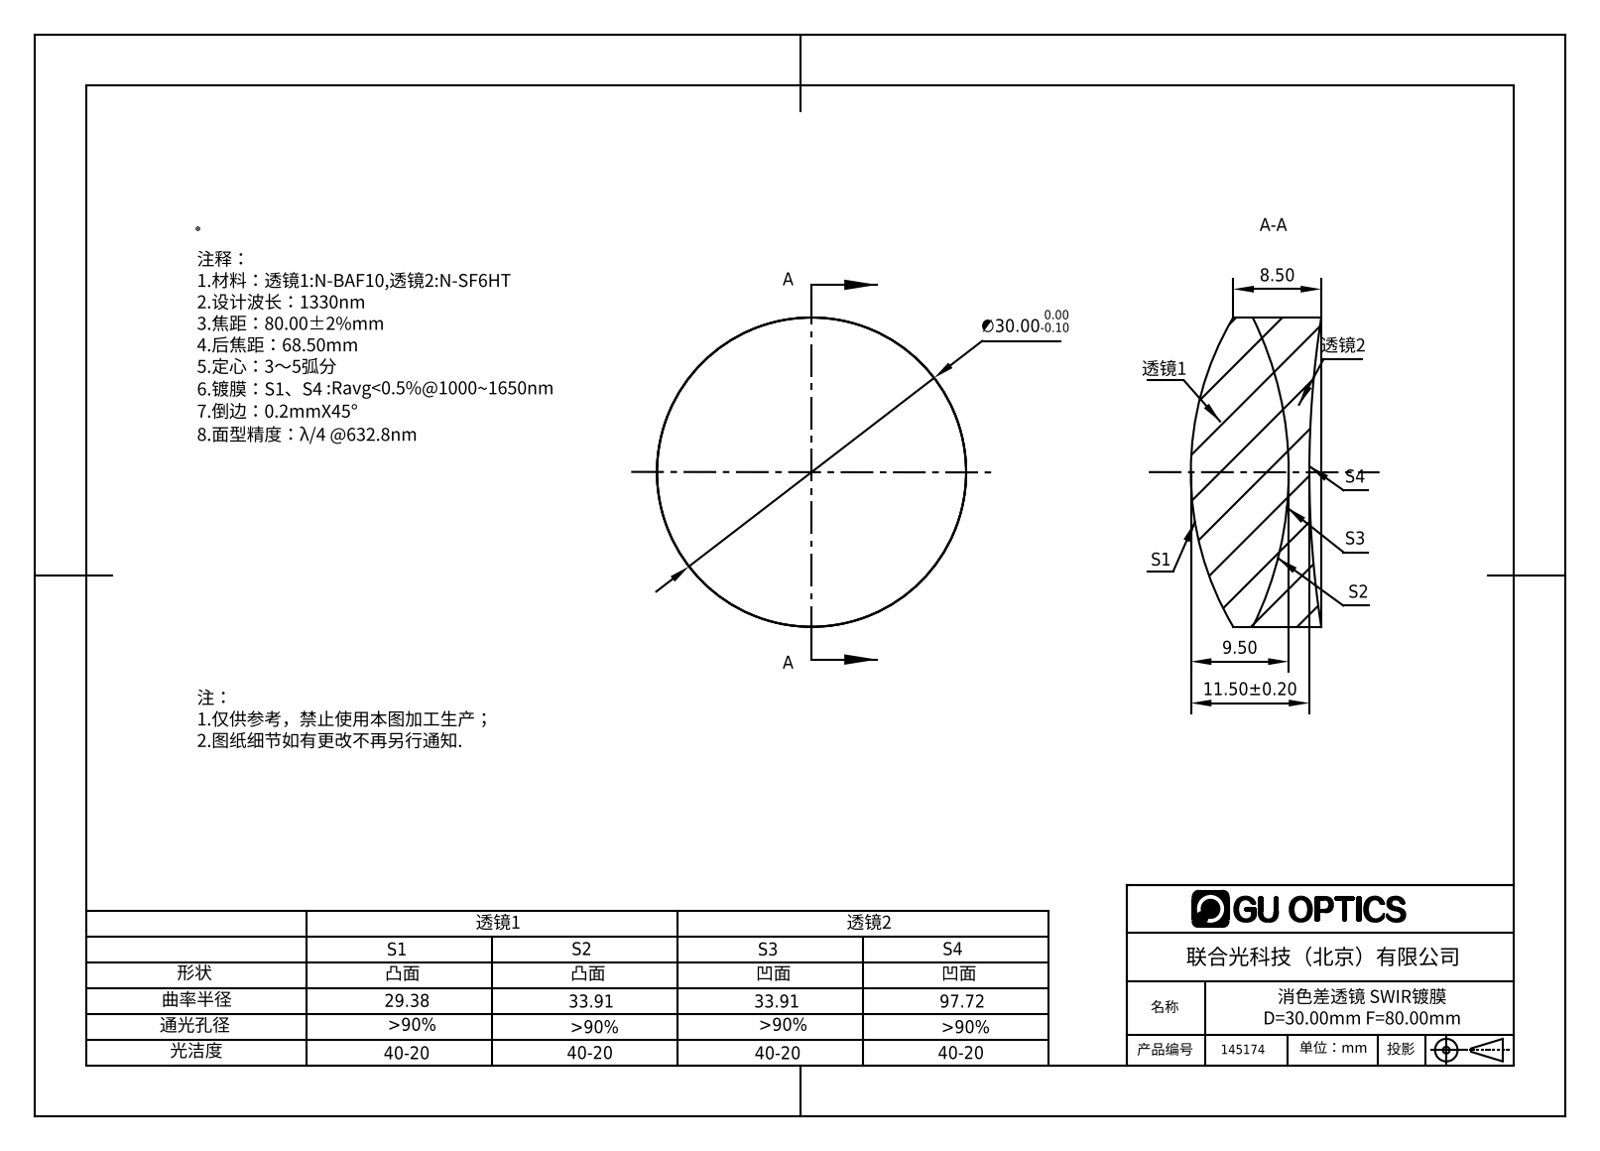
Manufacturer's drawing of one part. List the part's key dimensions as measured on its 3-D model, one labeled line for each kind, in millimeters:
Part name (STEP PRODUCT): 145174
STEP written by: SolidWorks 2016 (AUTOMOTIVE_DESIGN)
Units: millimetres
Bodies: 2 solids, 12 faces (0 planar, 4 cylindrical, 8 other)
Overall size (bounding box): 30 × 30 × 12.66
Volume: 7 119 mm³ · Surface area: 3 767 mm²
Round bosses / shafts (diameter × count): ⌀30 ×1
